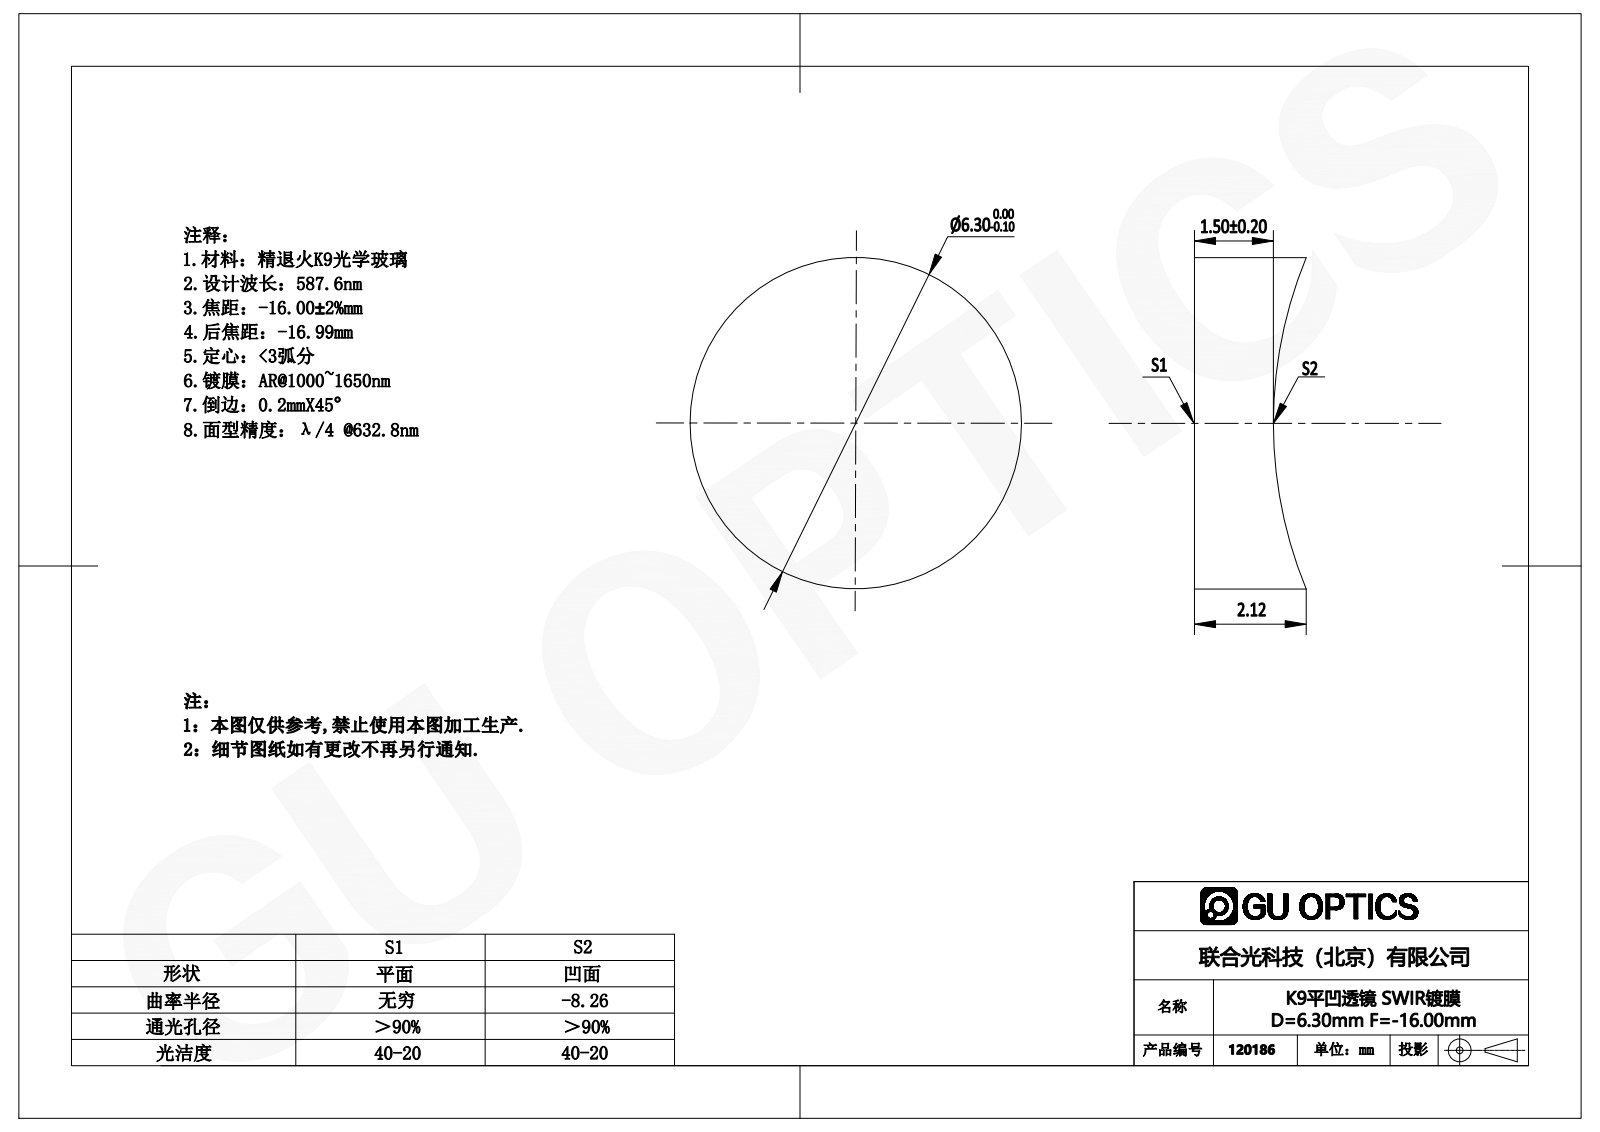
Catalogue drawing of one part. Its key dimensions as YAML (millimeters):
part_name: "120126"
step_written_by: "SolidWorks 2016 (AUTOMOTIVE_DESIGN)"
units: millimeters
bodies: {solids: 1, faces: 5, planar: 1, cylindrical: 2, other: 2}
overall_size: [6.3, 6.3, 2.12]
volume: 56
surface_area: 106
round_bosses_or_shafts:
  - {diameter: 6.3, count: 1}
